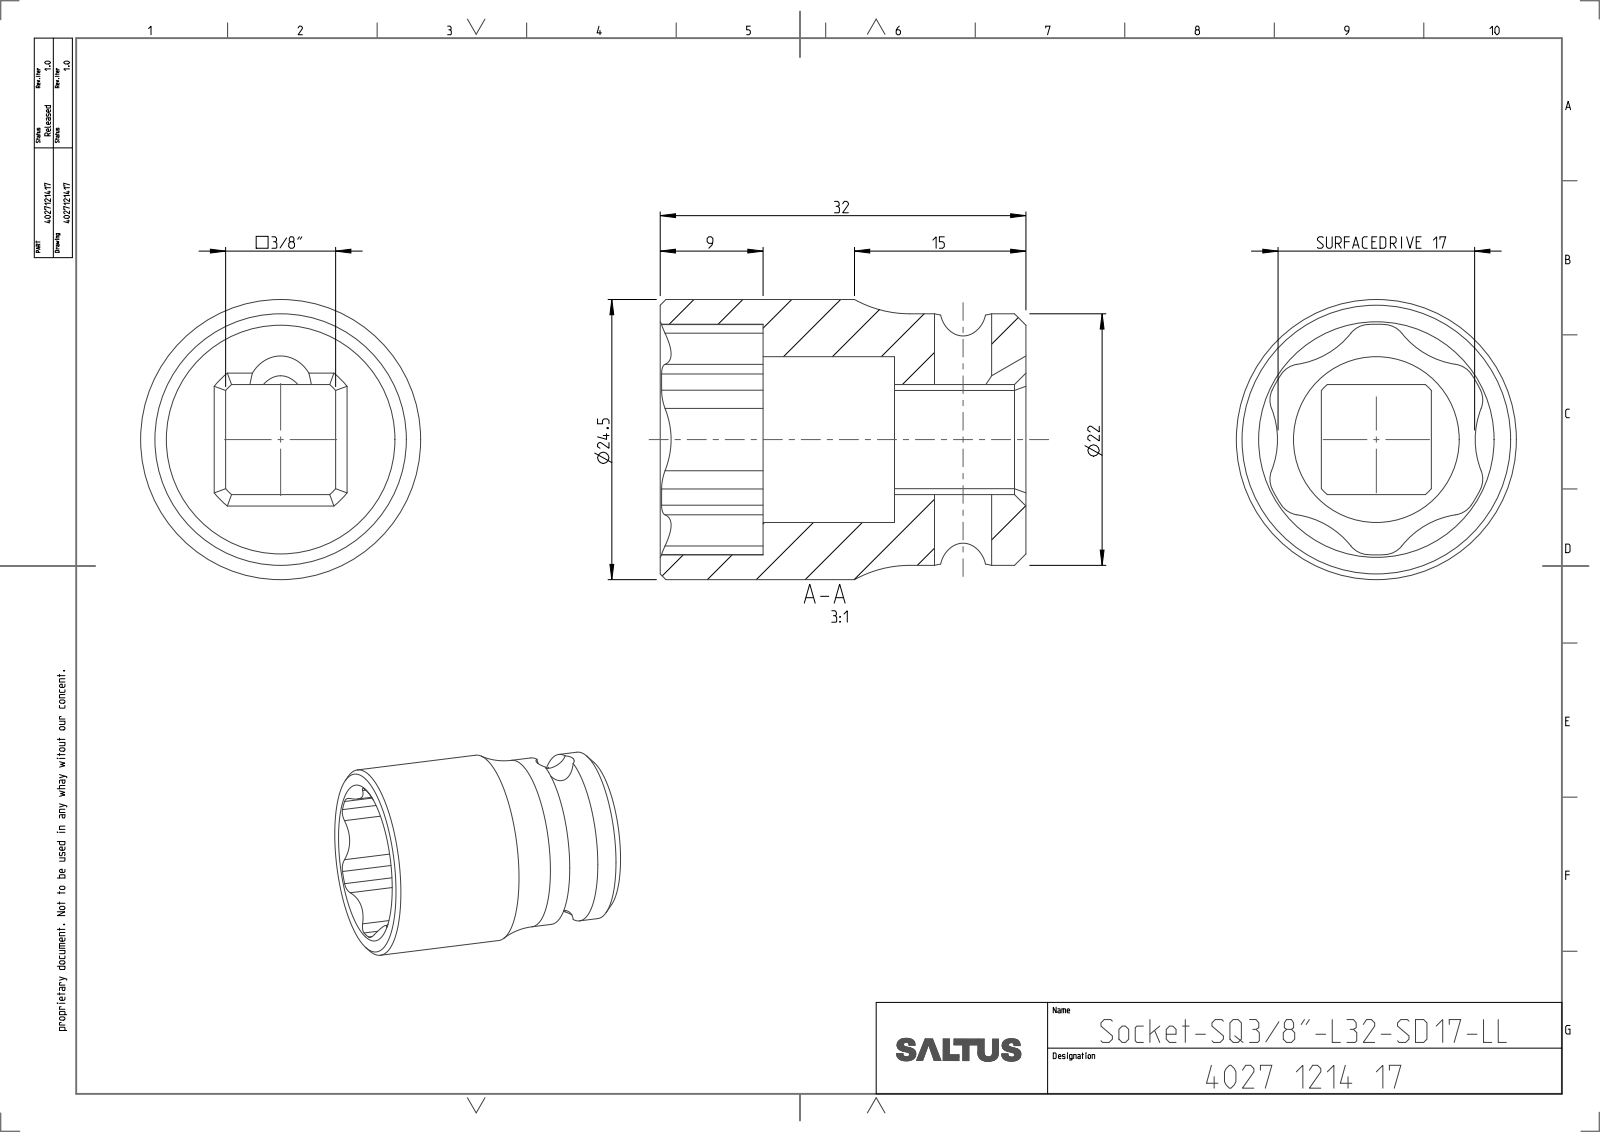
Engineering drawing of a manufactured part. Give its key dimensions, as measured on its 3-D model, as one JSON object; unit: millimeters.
{"part_name": "4027121417", "step_written_by": "CREO PARAMETRIC BY PTC INC, 2022414 (CONFIG_CONTROL_DESIGN)", "units": "millimeters", "bodies": {"solids": 1, "faces": 68, "planar": 13, "cylindrical": 41, "other": 14}, "overall_size": [32, 24.5, 24.5], "volume_mm3": 7790, "surface_area_mm2": 4599, "round_holes": [[5, 1], [14.5, 1]], "round_bosses_or_shafts": [[24.5, 1], [22, 1]], "partial_cylinders_radius": [[2, 12], [7.4, 6], [3, 1], [6.45, 1], [10.09, 1]], "face_to_face_distances": [9.62, 11.5, 23, 32, 9, 20.5]}
